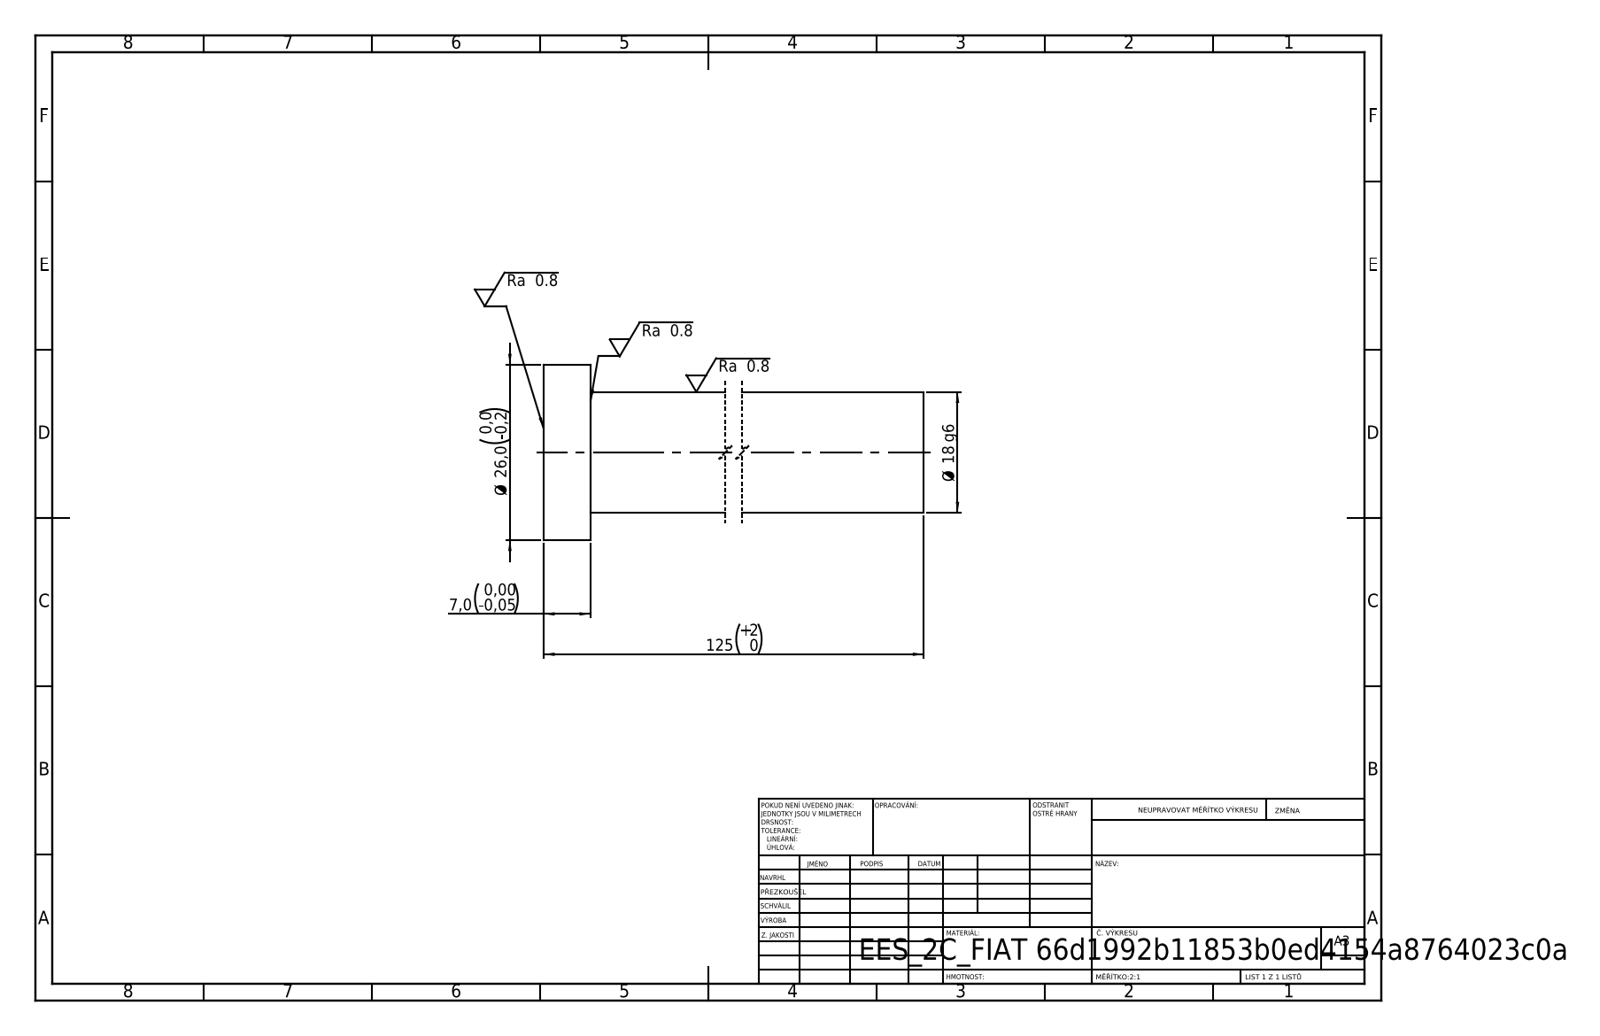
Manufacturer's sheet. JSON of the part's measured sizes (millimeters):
{"step_written_by": "SolidWorks 2019 (CONFIG_CONTROL_DESIGN)", "units": "millimeters", "bodies": {"solids": 1, "faces": 7, "planar": 3, "cylindrical": 4, "other": 0}, "overall_size": [125, 26, 26], "volume_mm3": 33744, "surface_area_mm2": 8306, "round_bosses_or_shafts": [[26, 1], [18, 1]], "face_to_face_distances": [7, 125, 118]}
